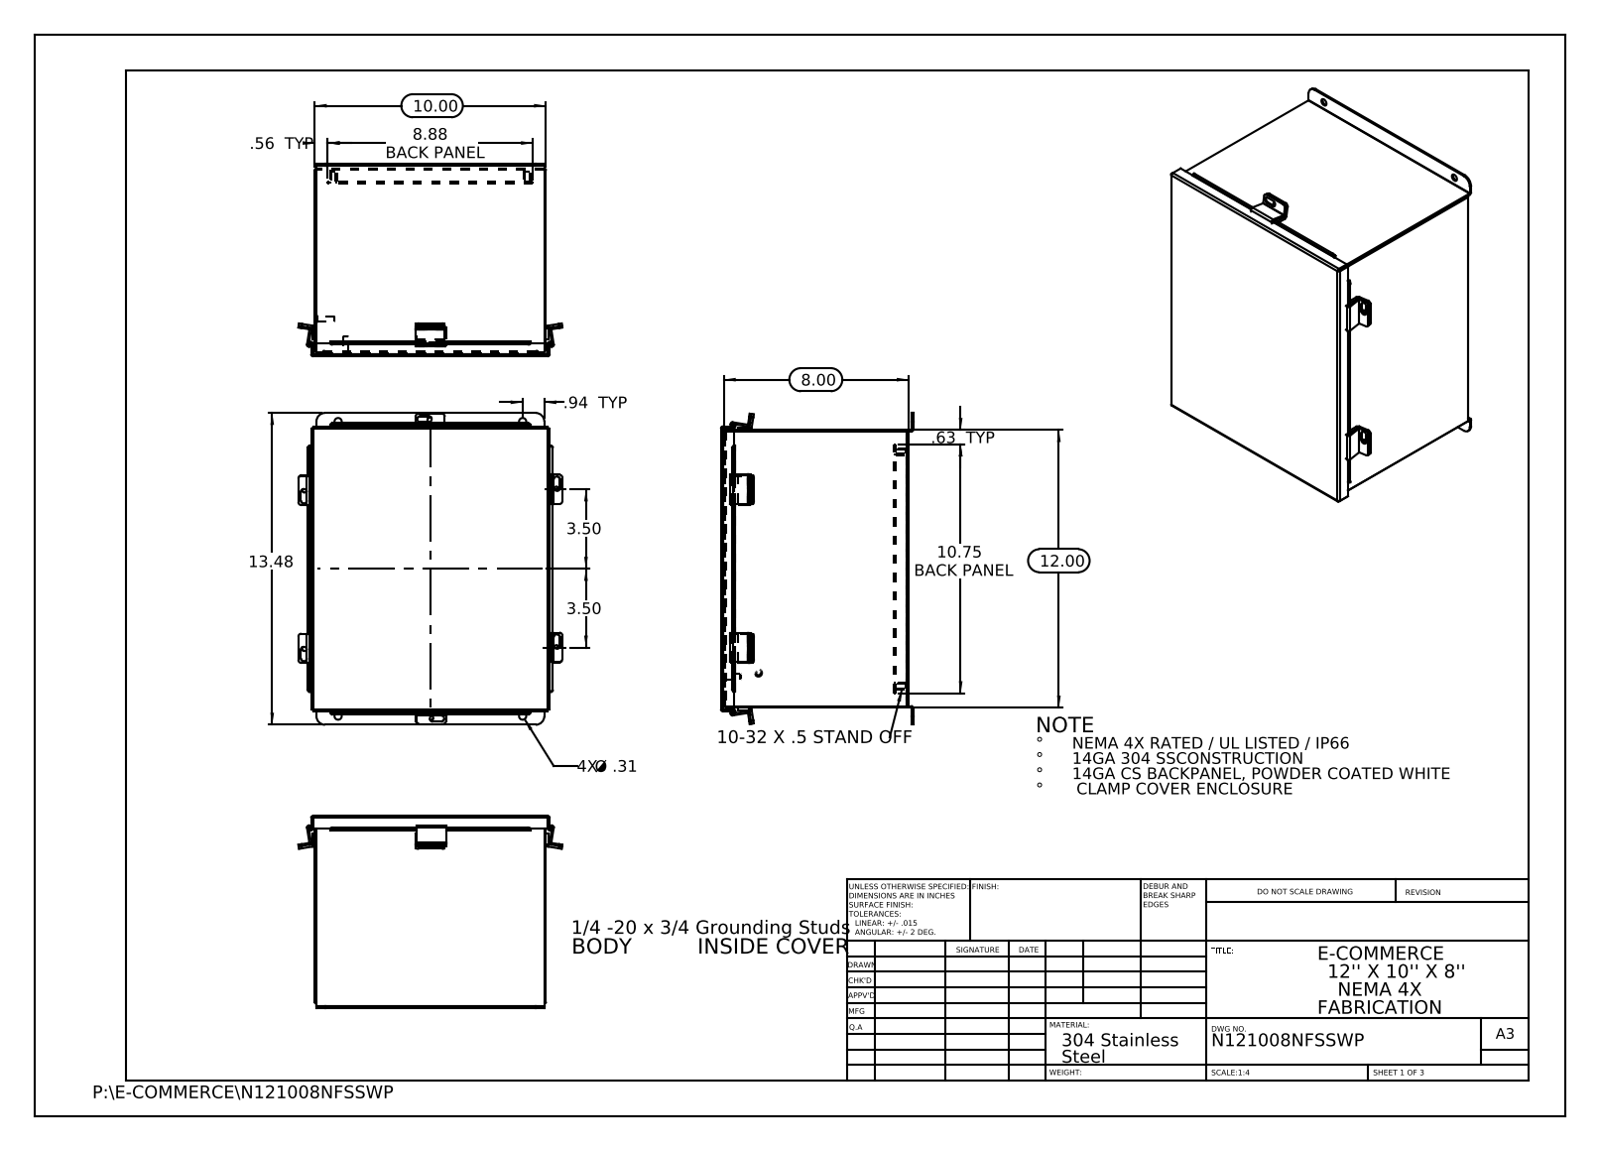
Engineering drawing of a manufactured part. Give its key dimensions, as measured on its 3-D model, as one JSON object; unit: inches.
{"part_name": "N121008NFSSWP JIC Backpanel; N121008NFSSWP JIC Cover Clamp; N121008NFSSWP JIC Clamp Bracket; N121008NFSSWP HW-CD-S-25020-034 (+6 more)", "step_written_by": "SolidWorks 2013 (CONFIG_CONTROL_DESIGN)", "units": "inches", "bodies": {"solids": 23, "faces": 548, "planar": 356, "cylindrical": 172, "other": 20}, "overall_size": [13.476, 11.407, 8.39], "volume_in3": 57.23, "surface_area_in2": 1551, "round_holes": [[0.25, 10], [0.187, 4], [0.312, 4]], "round_bosses_or_shafts": [[0.313, 4], [0.315, 2], [0.236, 2]], "partial_cylinders_radius": [[0.125, 23], [0.009, 16], [0.013, 12], [0.088, 12], [0.133, 12], [0.083, 8], [0.1, 8], [0.084, 4]], "face_to_face_distances": [0.075, 8.128, 9.925, 11.925, 8.053, 8.203, 0.074, 0.575, 0.5, 7.553], "hole_center_spacings": [1.315, 8.278, 11.428, 14.05, 6.85, 7.976, 8.375, 10.126]}
